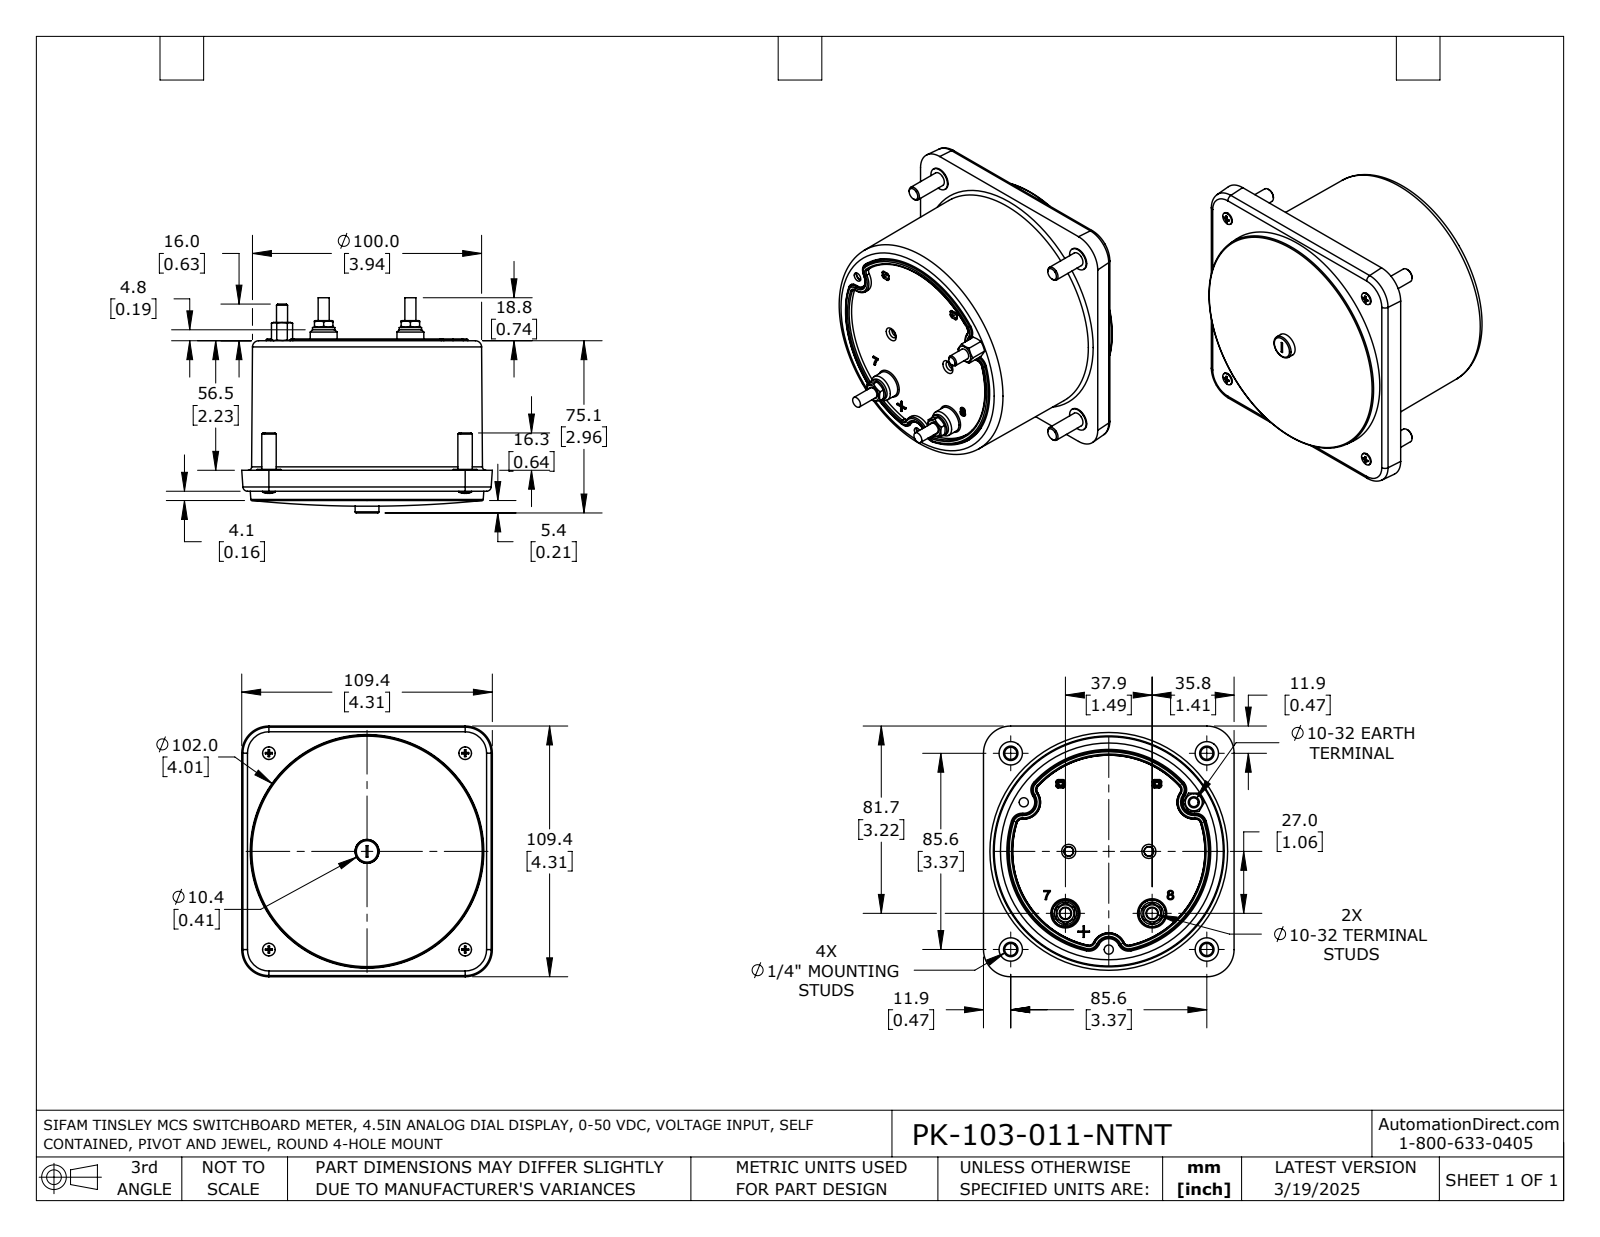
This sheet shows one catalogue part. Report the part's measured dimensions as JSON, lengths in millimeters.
{"part_name": "PK-103-011-NTNT", "step_written_by": "SolidWorks 2021 (AUTOMOTIVE_DESIGN)", "units": "millimeters", "bodies": {"solids": 1, "faces": 609, "planar": 167, "cylindrical": 141, "other": 301}, "overall_size": [109.4, 109.4, 93.9], "volume_mm3": 594500, "surface_area_mm2": 53040, "round_holes": [[2.4, 4], [3.5, 4], [8, 4], [4, 3], [5.3, 2]], "round_bosses_or_shafts": [[10.2, 4], [6.3, 4], [5.5, 4], [2.9, 4], [4.8, 3], [9.8, 2], [3.7, 1]], "partial_cylinders_radius": [[0.5, 24], [4.8, 9], [2, 4], [44.5, 1]], "face_to_face_distances": [55.3, 64.4, 9.1, 1.2, 56.5, 65.7, 12.4, 69, 67.7, 3.3], "hole_center_spacings": [85.6, 85.6, 85.7, 85.8, 85.9, 121.1, 24.7, 28.6]}
